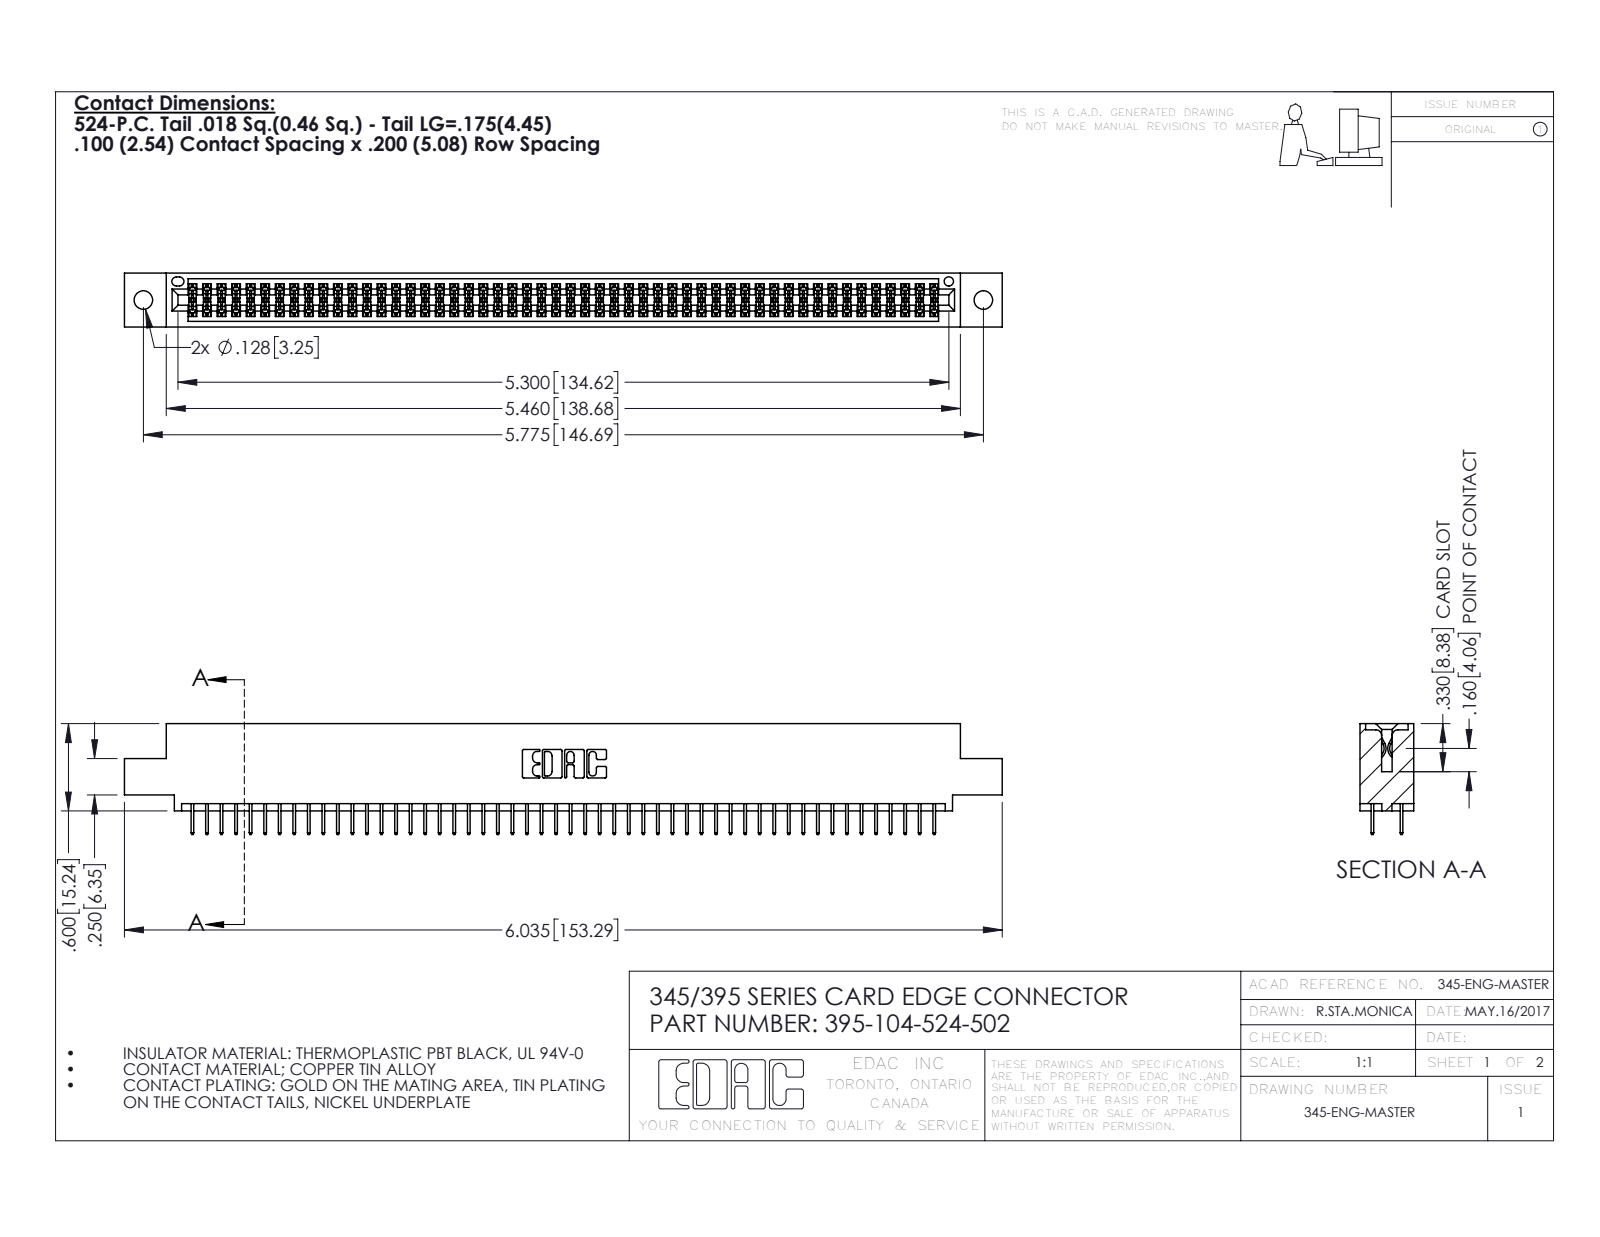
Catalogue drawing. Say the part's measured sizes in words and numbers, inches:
The part is named "345 Part_0.110 Offset - 0.128 Dia; 395-104-524-502; 345-292-001_345-293-124". Its 3-D file was written by "SolidWorks 2016 (CONFIG_CONTROL_DESIGN)". It is 105 solids with 5746 faces: 4140 planar, 1606 cylindrical and 0 other. Overall it measures 6.035 by 0.762 by 0.37 inches. Its volume is 0.898 cubic inches and its surface area 33.09 square inches. Round holes: 2 of diameter 0.128, 1 of diameter 0.064. Partial cylindrical surfaces (rounded edges, fillets, slot ends): 156 of radius 0.006, 22 of radius 0.01, 6 of radius 0.007, 6 of radius 0.031, 3 of radius 0.026, 2 of radius 0.014, 2 of radius 0.019, 2 of radius 0.022. The main face-to-face distances are 0.072, 0.298, 0.2, 0.37, 0.098, 0.272, 0.025, 0.225, 0.072, 0.175. The hole center spacings are 0.27, 5.539, 5.775.
